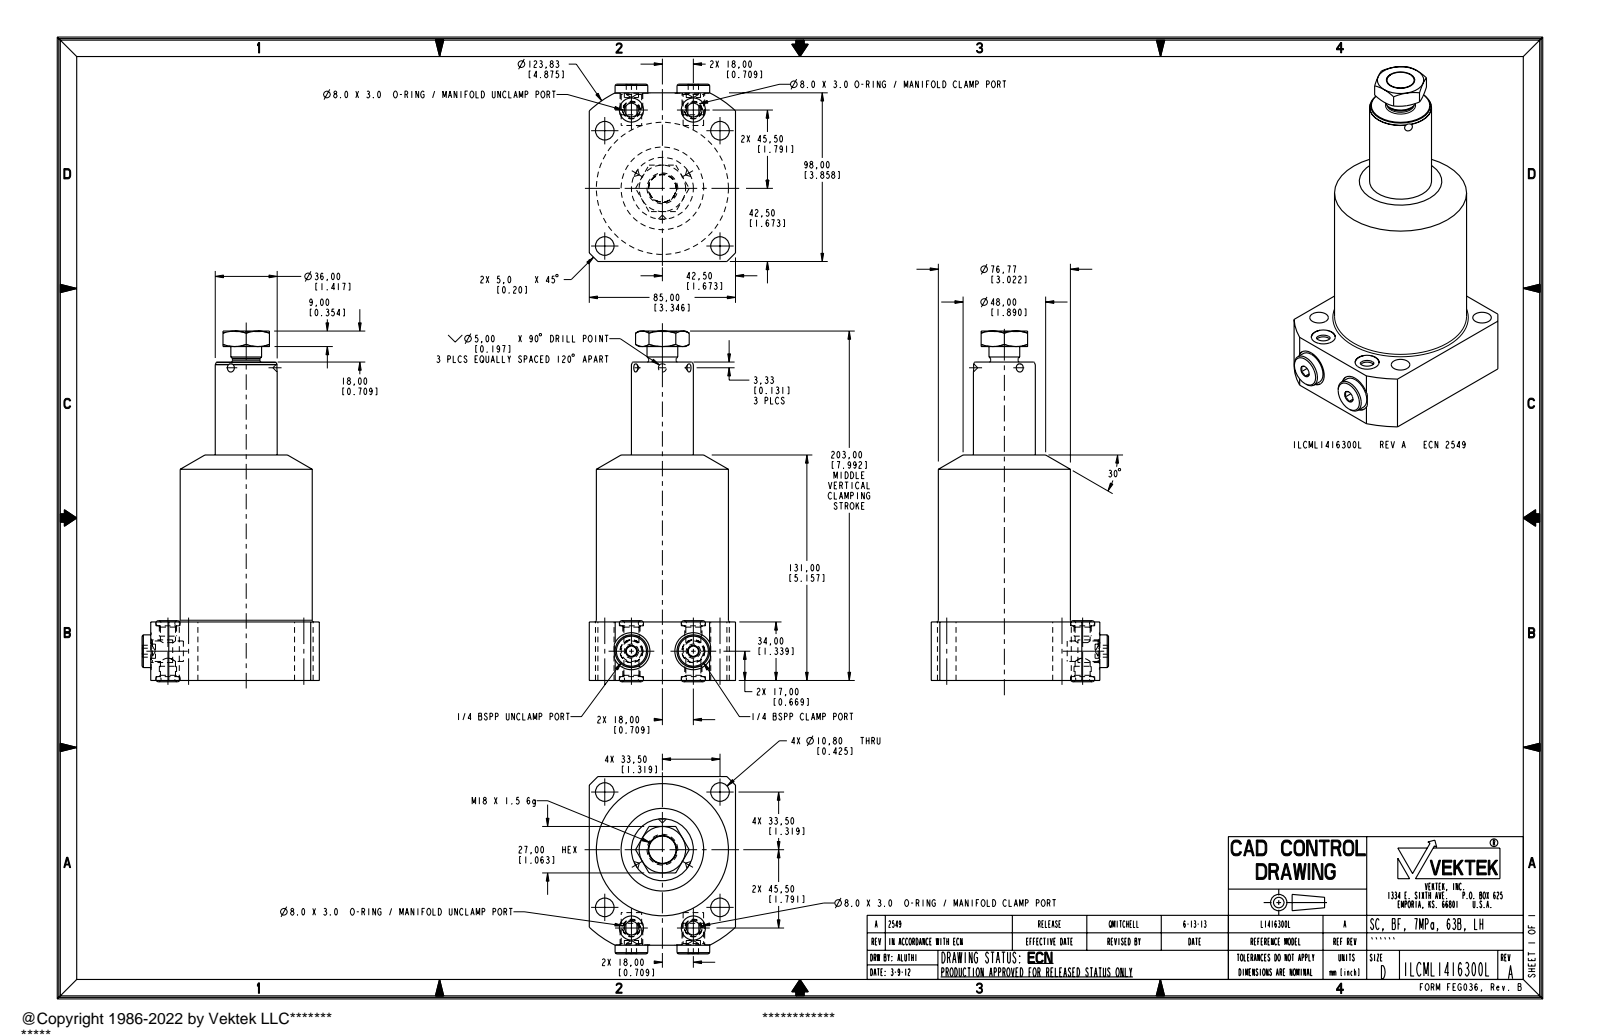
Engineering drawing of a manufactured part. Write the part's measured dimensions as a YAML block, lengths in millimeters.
part_name: "ILCML1416300L"
step_written_by: "PRO/ENGINEER BY PARAMETRIC TECHNOLOGY CORPORATION, 2007460 (AUTOMOTIVE_DESIGN_CC2)"
units: millimeters
bodies: {solids: 5, faces: 214, planar: 67, cylindrical: 62, other: 85}
overall_size: [203.75, 103.05, 85]
volume: 760016
surface_area: 68935
round_holes:
  - {diameter: 10.8, count: 4}
  - {diameter: 8.75, count: 2}
  - {diameter: 11.89, count: 2}
  - {diameter: 14, count: 2}
  - {diameter: 21.5, count: 2}
  - {diameter: 16.5, count: 1}
round_bosses_or_shafts:
  - {diameter: 19, count: 2}
  - {diameter: 13.16, count: 2}
  - {diameter: 10, count: 2}
  - {diameter: 8.25, count: 2}
  - {diameter: 76.77, count: 1}
  - {diameter: 36, count: 1}
  - {diameter: 17.87, count: 1}
  - {diameter: 16, count: 1}
partial_cylinders:
  - {radius: 61.91, count: 1}
face_to_face_distances: [85, 34, 98, 131, 97, 185, 151, 54, 9, 18]
hole_center_spacings: [47.38, 67, 19.6, 36, 48.93, 52.88, 80.51, 94.3]
